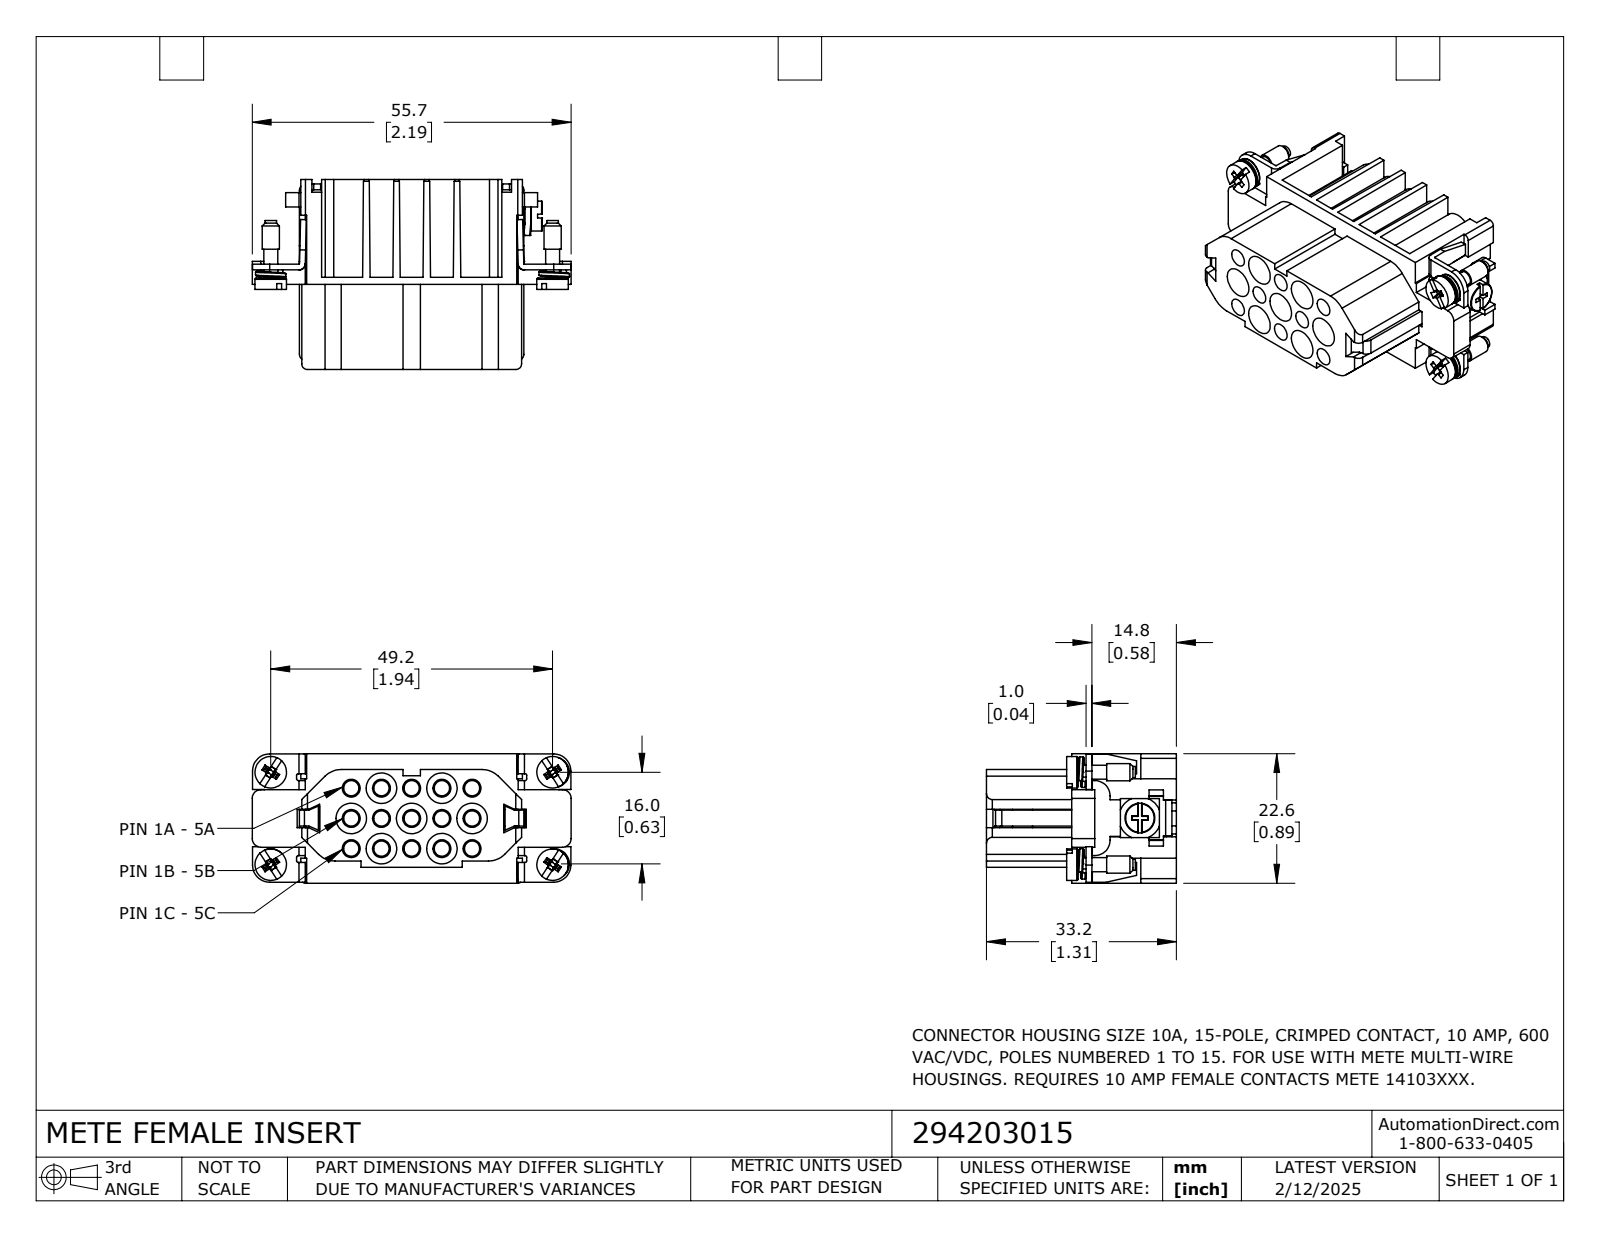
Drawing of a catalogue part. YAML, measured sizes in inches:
part_name: "294203015"
step_written_by: "SolidWorks 2024 (CONFIG_CONTROL_DESIGN)"
units: inches
bodies: {solids: 13, faces: 855, planar: 482, cylindrical: 322, other: 51}
overall_size: [2.192, 1.306, 0.89]
volume: 0.955
surface_area: 26.12
round_holes:
  - {diameter: 0.105, count: 15}
  - {diameter: 0.123, count: 15}
  - {diameter: 0.154, count: 15}
  - {diameter: 0.166, count: 15}
  - {diameter: 0.21, count: 7}
  - {diameter: 0.098, count: 5}
  - {diameter: 0.114, count: 4}
  - {diameter: 0.118, count: 1}
round_bosses_or_shafts:
  - {diameter: 0.217, count: 4}
  - {diameter: 0.209, count: 4}
  - {diameter: 0.118, count: 4}
  - {diameter: 0.096, count: 4}
  - {diameter: 0.079, count: 4}
  - {diameter: 0.205, count: 1}
  - {diameter: 0.114, count: 1}
partial_cylinders:
  - {radius: 0.01, count: 32}
  - {radius: 0.012, count: 12}
  - {radius: 0.004, count: 10}
  - {radius: 0.043, count: 10}
  - {radius: 0.123, count: 10}
  - {radius: 0.059, count: 6}
  - {radius: 0.032, count: 4}
  - {radius: 0.04, count: 4}
face_to_face_distances: [0.039, 0.415, 0.208, 0.673, 0.109, 0.781, 0.113, 1.351, 0.586, 1.306]
hole_center_spacings: [0.415, 0.207, 0.208, 0.464, 0.465, 0.294, 0.587, 0.63]
